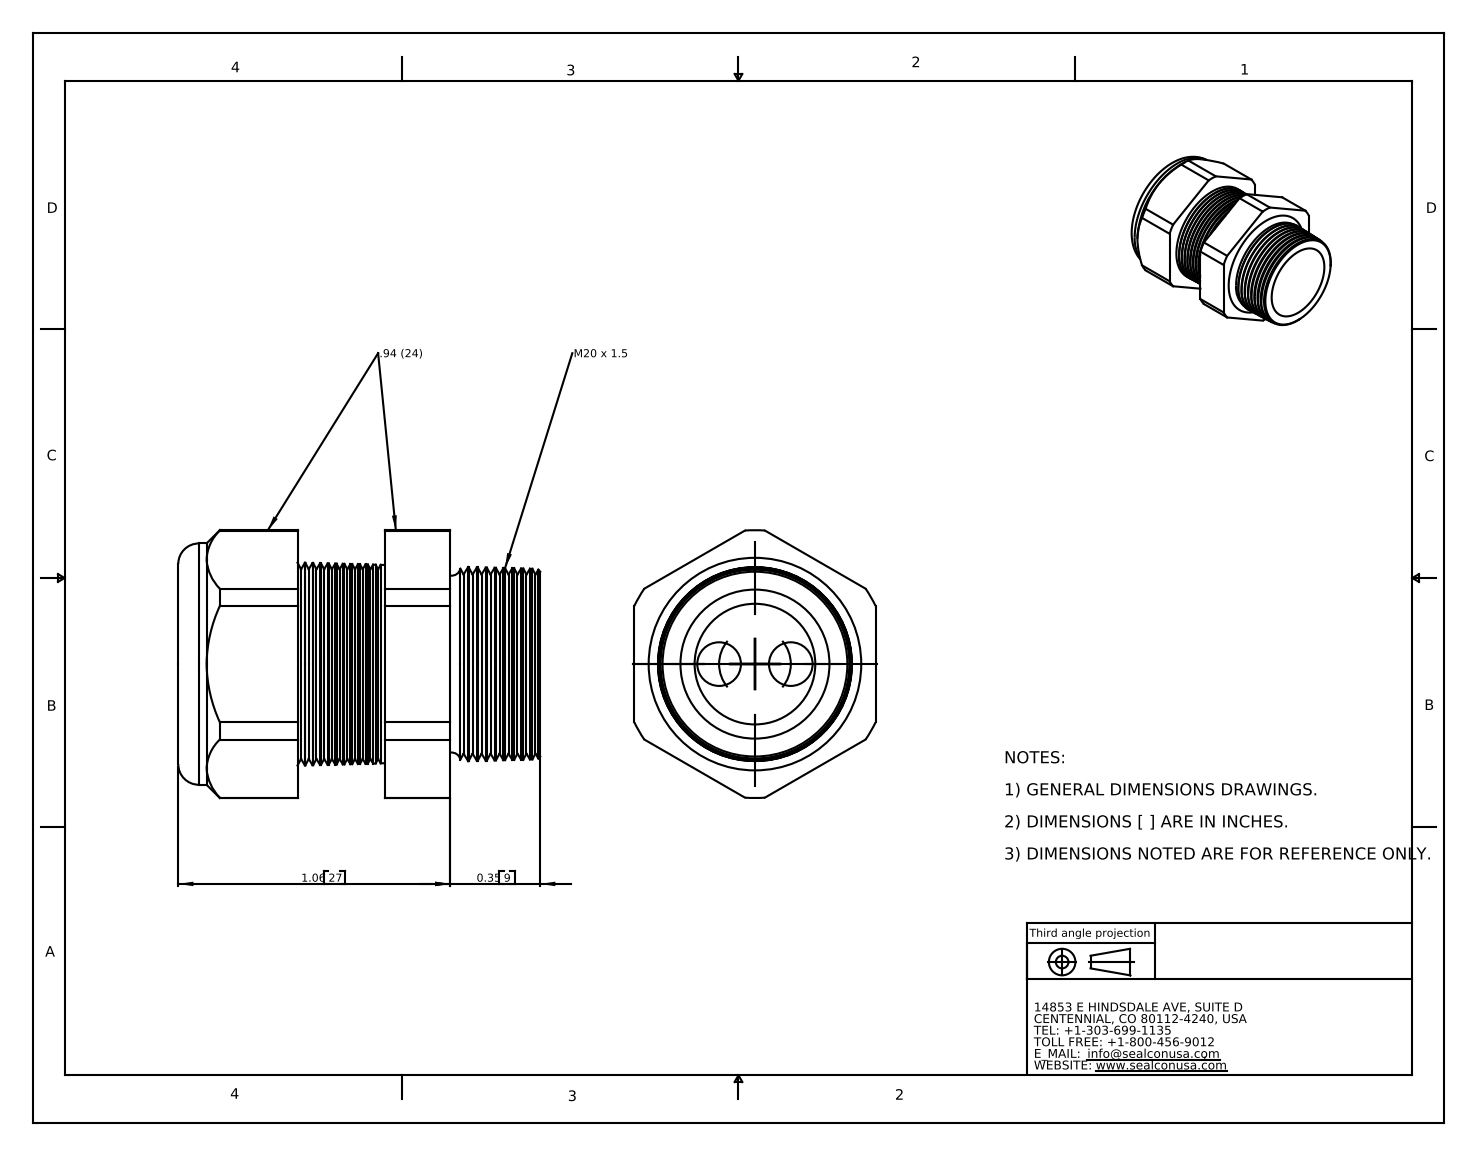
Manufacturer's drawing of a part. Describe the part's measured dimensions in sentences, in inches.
The part is named "CD20M8-GY". Its 3-D file was written by "SolidWorks 2007 (CONFIG_CONTROL_DESIGN)". It is 2 solids with 178 faces: 20 planar, 24 cylindrical and 134 other. Overall it measures 1.41 by 1.043 by 0.94 inches. Its volume is 0.575 cubic inches and its surface area 9.895 square inches. Round holes: 2 of diameter 0.17, 1 of diameter 0.45, 1 of diameter 0.47. Round bosses or shafts: 1 of diameter 0.94. Partial cylindrical surfaces (rounded edges, fillets, slot ends): 1 of radius 0.522. The main face-to-face distances are 0.94, 0.804, 0.465, 0.34, 1.06, 0.596, 0.256, 1.41, 0.946, 0.606. The hole center spacings are 0.14, 0.28.
